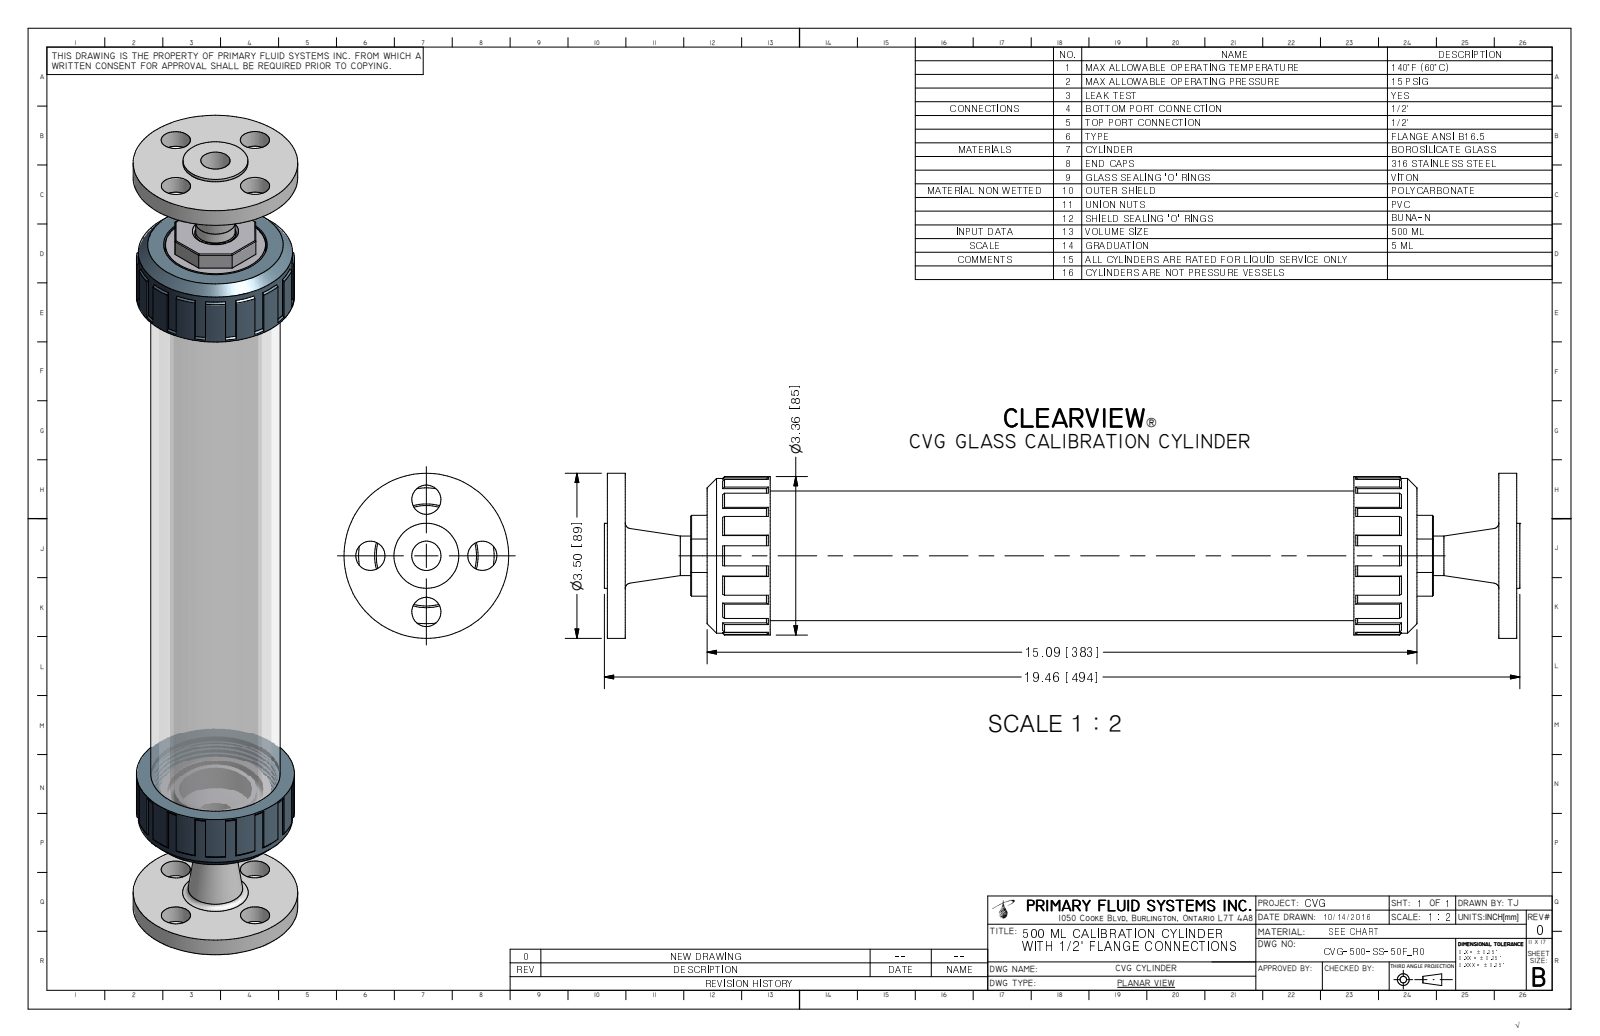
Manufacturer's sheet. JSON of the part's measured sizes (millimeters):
{"part_name": "CVG-500-SS-50F_R0; CVG-3-500-METAL-S-50_R1; CVG-6-500; CVG-1-500-A_R0 (+2 more)", "step_written_by": "Autodesk Inventor 2009 (AUTOMOTIVE_DESIGN)", "units": "millimeters", "bodies": {"solids": 8, "faces": 341, "planar": 96, "cylindrical": 53, "other": 192}, "overall_size": [494.3, 88.9, 88.9], "volume_mm3": 782300, "surface_area_mm2": 377400, "round_holes": [[15.7, 4], [15.8, 1], [17.9, 1], [22.4, 1], [39.5, 1], [46, 1], [52.1, 1], [61, 1]], "round_bosses_or_shafts": [[88.9, 1], [69.9, 1], [67.6, 1], [67.6, 1], [63.2, 1], [59.9, 1], [56.5, 1], [54.1, 1]], "face_to_face_distances": [9.7, 481.5, 491.1, 471.8, 45, 446.1, 35.4, 436.4, 78, 413.1], "hole_center_spacings": [30.2, 42.7, 60.5]}
